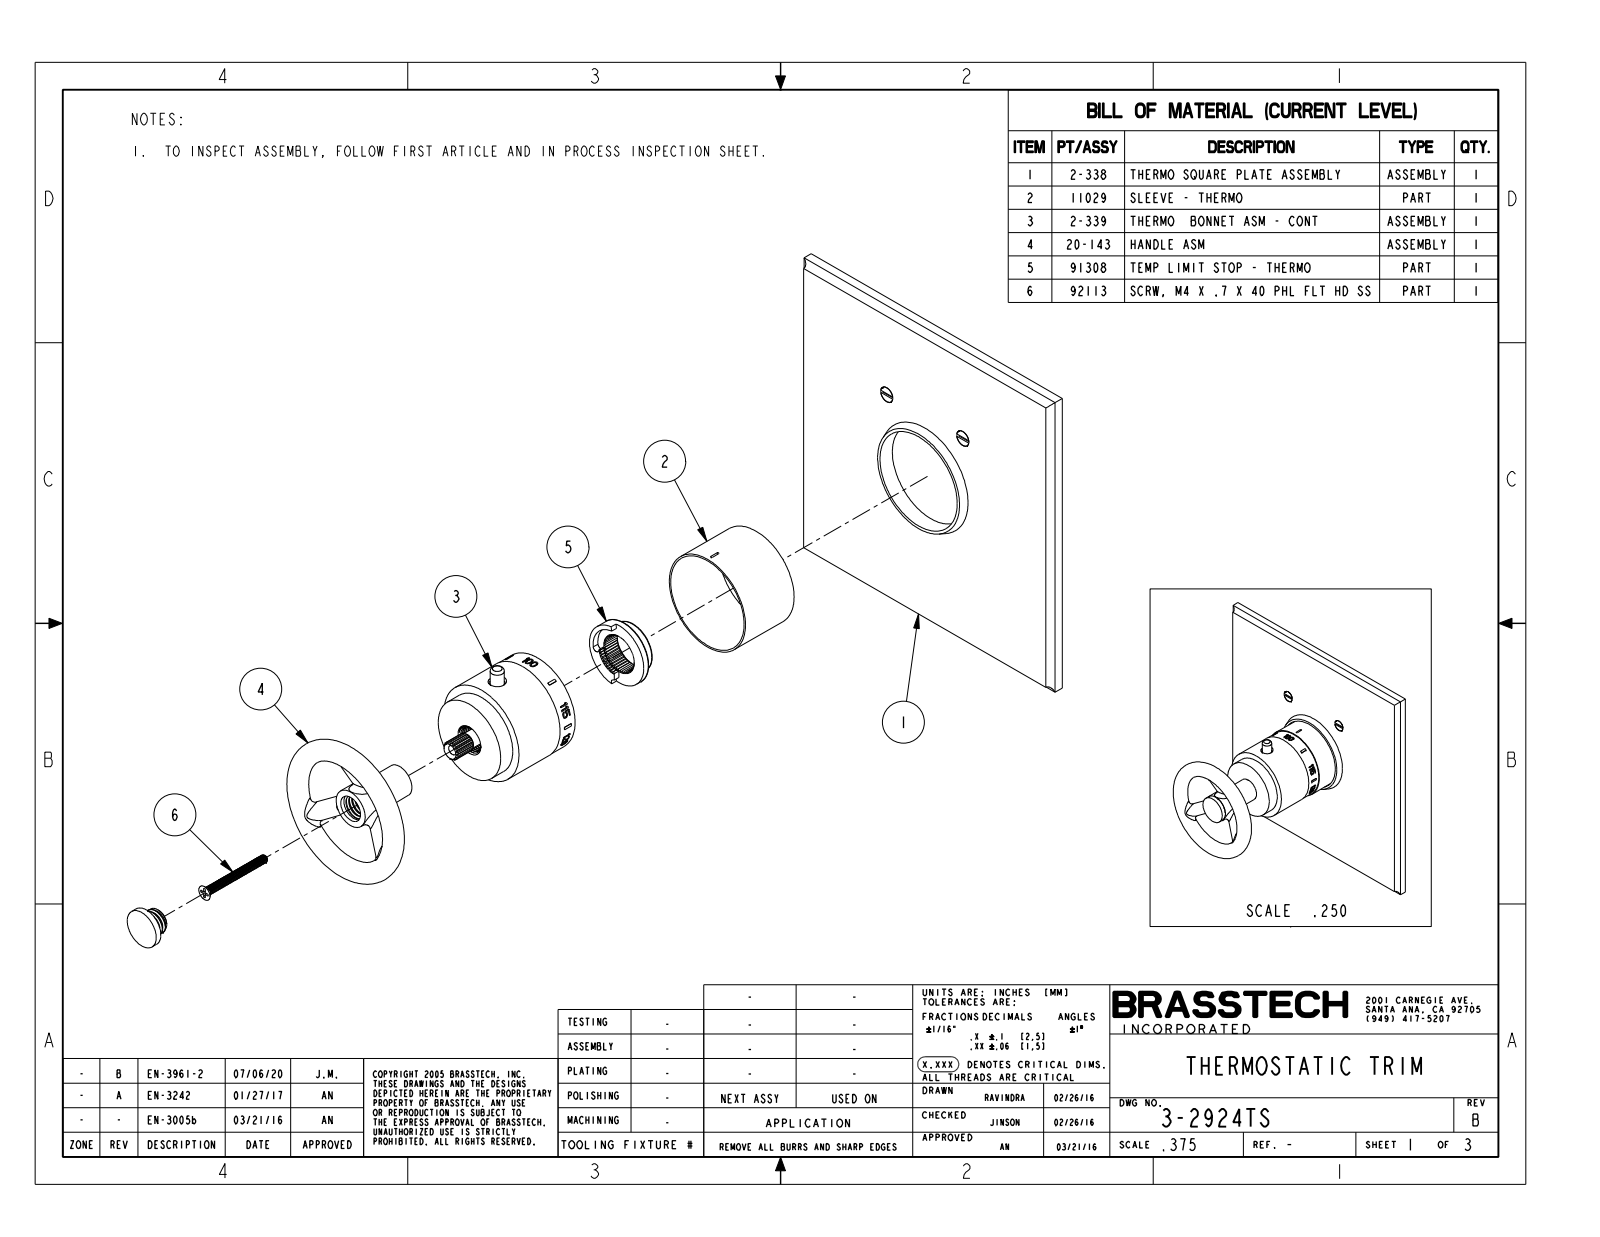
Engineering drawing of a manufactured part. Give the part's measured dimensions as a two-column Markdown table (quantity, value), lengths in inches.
| quantity | value |
| --- | --- |
| part name | 3-2924TS |
| STEP written by | CREO PARAMETRIC BY PTC INC, 2018400 (CONFIG_CONTROL_DESIGN) |
| units | inches |
| bodies | 1 solid, 407 faces (334 planar, 45 cylindrical, 28 other) |
| overall size | 6.5 × 6.5 × 4.443 |
| volume | 22.08 in³ |
| surface area | 121.6 in² |
| round bosses / shafts (diameter × count) | 0.35 × 3, 1.97 × 1, 1.94 × 1, 1.929 × 1, 1.615 × 1, 0.75 × 1, 0.63 × 1, 0.26 × 1 |
| partial cylindrical surfaces (radius × count) | 0.125 × 4, 0.969 × 1 |
| main face-to-face distances | 0.313, 6.5, 2.843, 2.53, 2.531, 2.219, 0.312, 0.159, 0.472, 2.059 |
